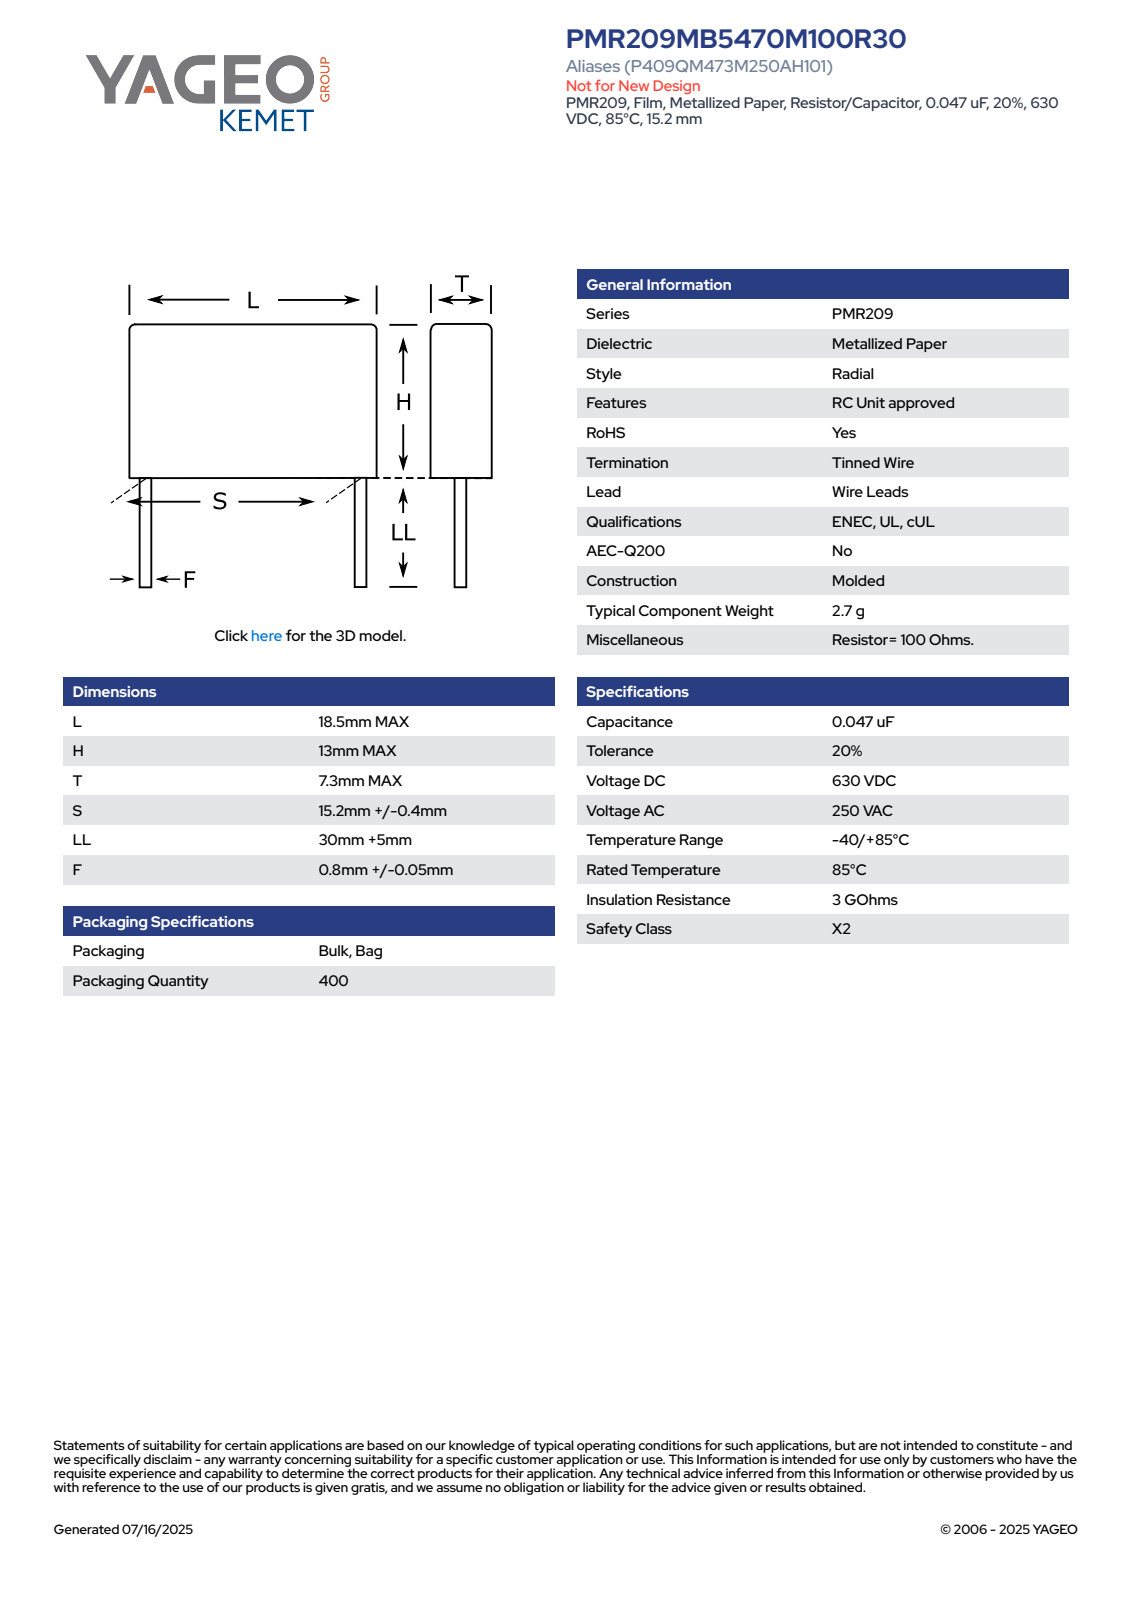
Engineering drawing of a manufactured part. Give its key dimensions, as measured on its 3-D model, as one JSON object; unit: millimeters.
{"part_name": "CFR_MOLDED_18.5X13X7.3_L18.5H13T7.3S15.2LL35F0.85", "step_written_by": "SolidWorks 2014 (AUTOMOTIVE_DESIGN)", "units": "millimeters", "bodies": {"solids": 4, "faces": 73, "planar": 65, "cylindrical": 8, "other": 0}, "overall_size": [48, 18.5, 7.3], "volume_mm3": 1793, "surface_area_mm2": 1133, "round_bosses_or_shafts": [[0.85, 2]], "partial_cylinders_radius": [[0.5, 4]], "face_to_face_distances": [7.3, 13, 18.5, 35, 48, 1.66, 42.11, 7.11, 5.89, 40.45]}
